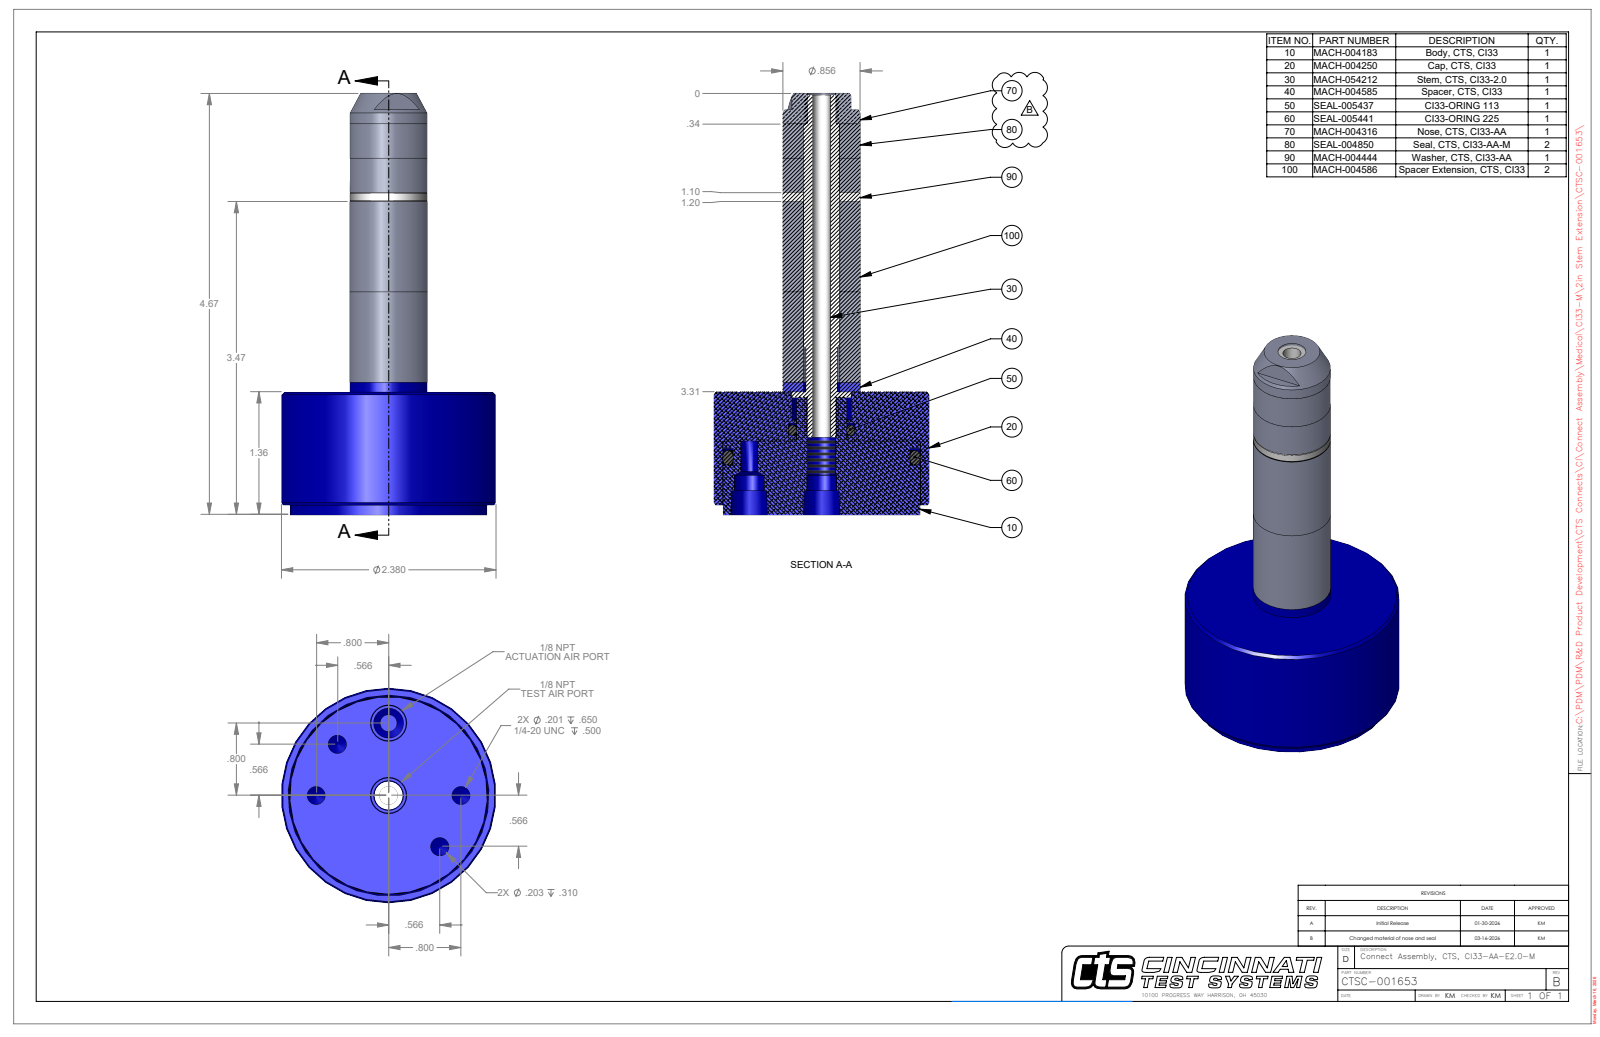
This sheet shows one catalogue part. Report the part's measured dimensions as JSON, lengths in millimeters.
{"part_name": "CTSC-001653", "step_written_by": "SolidWorks 2023 (AUTOMOTIVE_DESIGN)", "units": "millimeters", "bodies": {"solids": 8, "faces": 78, "planar": 37, "cylindrical": 28, "other": 13}, "overall_size": [118.54, 60.45, 60.45], "volume_mm3": 124185, "surface_area_mm2": 30053, "round_holes": [[5.11, 2], [5.16, 2], [5.16, 1], [7.94, 1], [8.43, 1], [9.91, 1], [10.24, 1], [16.74, 1], [55.58, 1]], "round_bosses_or_shafts": [[60.45, 1], [55.32, 1], [21.79, 1], [21.74, 1], [16.51, 1], [9.93, 1], [9.53, 1]], "face_to_face_distances": [34.54, 25.4, 109.91, 75.37, 100.25, 65.71, 9.66, 37.31, 2.77, 62.94], "hole_center_spacings": [20.32, 15.55, 37.55, 40.64]}
